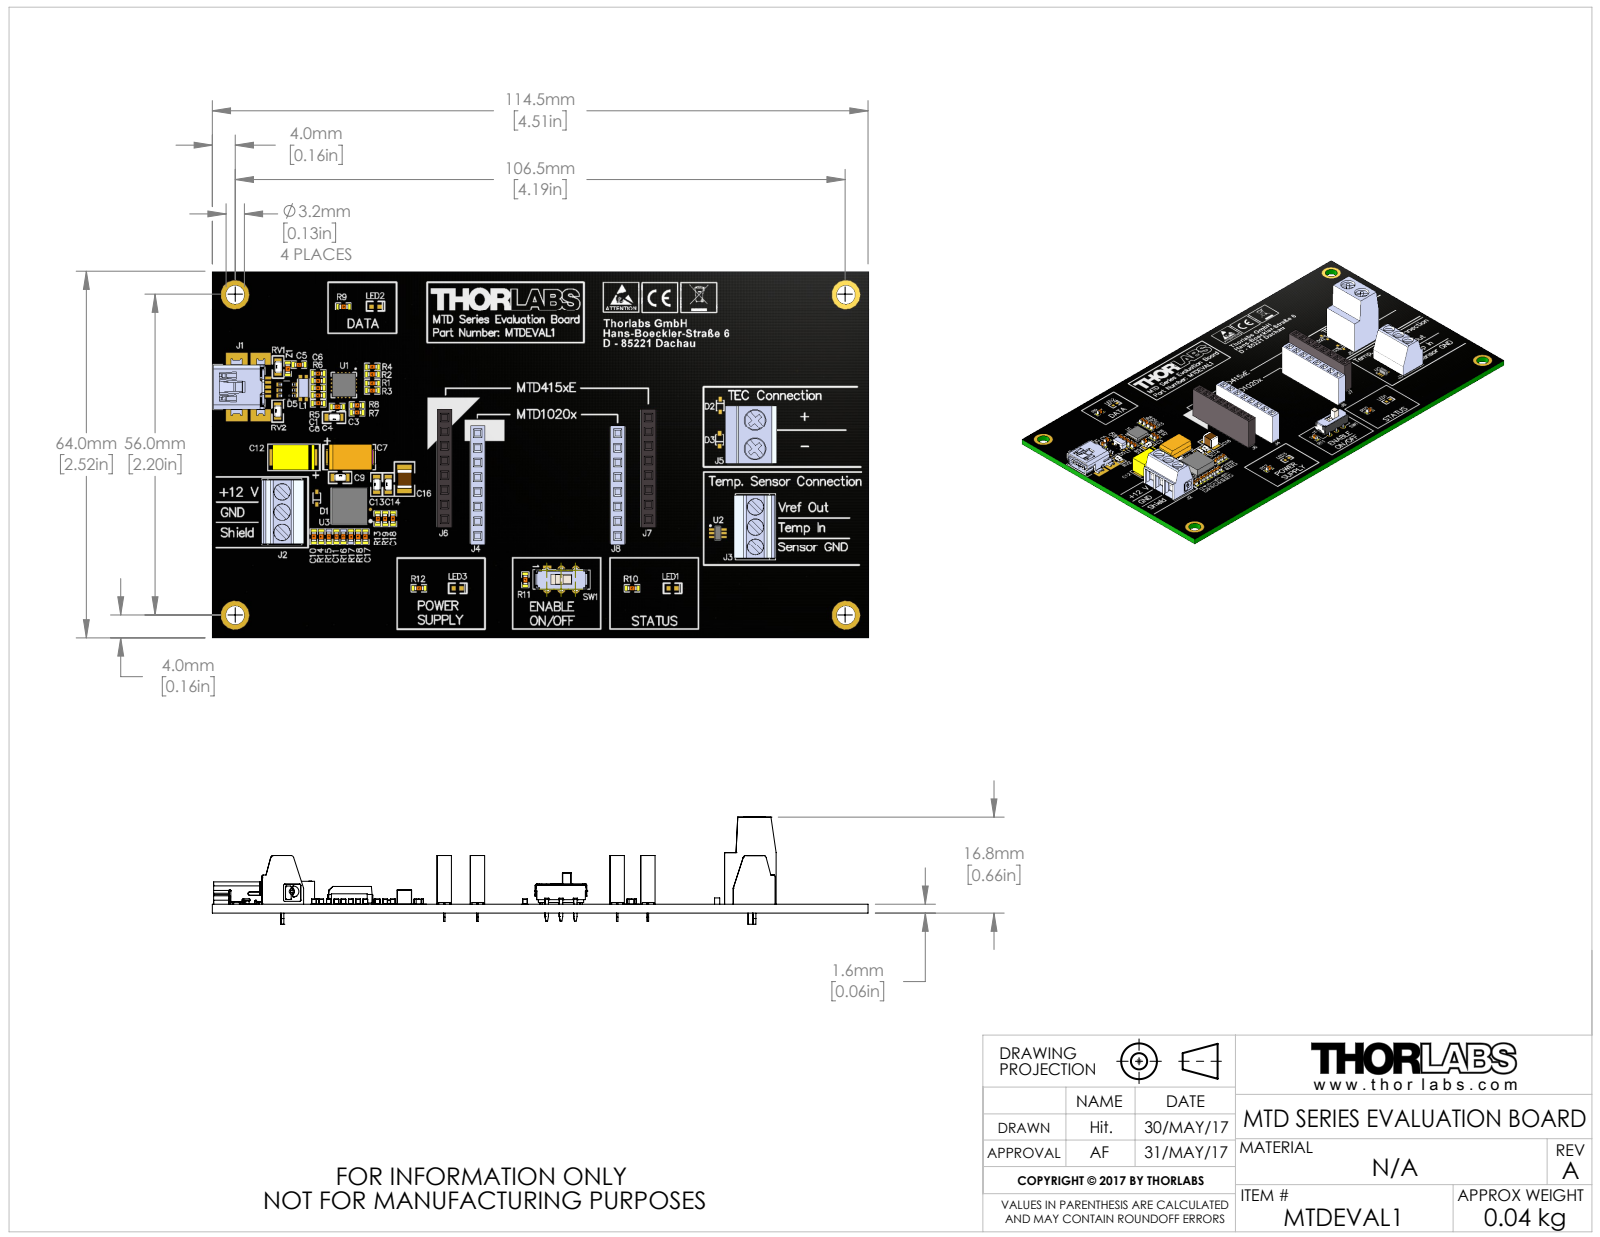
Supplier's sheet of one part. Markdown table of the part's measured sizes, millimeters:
| quantity | value |
| --- | --- |
| part name | MTN00xxxx-E0W |
| STEP written by | SolidWorks 2016 (AUTOMOTIVE_DESIGN) |
| units | millimeters |
| bodies | 0 solids, 4986 faces (2910 planar, 1115 cylindrical, 961 other) |
| overall size | 114.5 × 64 × 18.7 |
| round holes (diameter × count) | 0.9 × 40, 1.2 × 6, 2.9 × 6, 3.2 × 4, 1.4 × 2, 3.8 × 2, 0.5 × 1 |
| round bosses / shafts (diameter × count) | 2.8 × 6, 1.1 × 6, 3.53 × 2, 0.8 × 2, 0.46 × 2 |
| partial cylindrical surfaces (radius × count) | 0.15 × 73, 0.1 × 36, 0.5 × 22, 0.16 × 20, 0.3 × 17, 0.2 × 16, 1.5 × 10, 0.21 × 8 |
| main face-to-face distances | 1.55, 2.5, 5.8, 30.2, 35.56, 5.36, 24.4, 29.76, 3.3, 1.85 |
| hole center spacings | 2.54, 5.08, 7.62, 6.09, 10.16, 5.37, 7.64, 5.79 |
